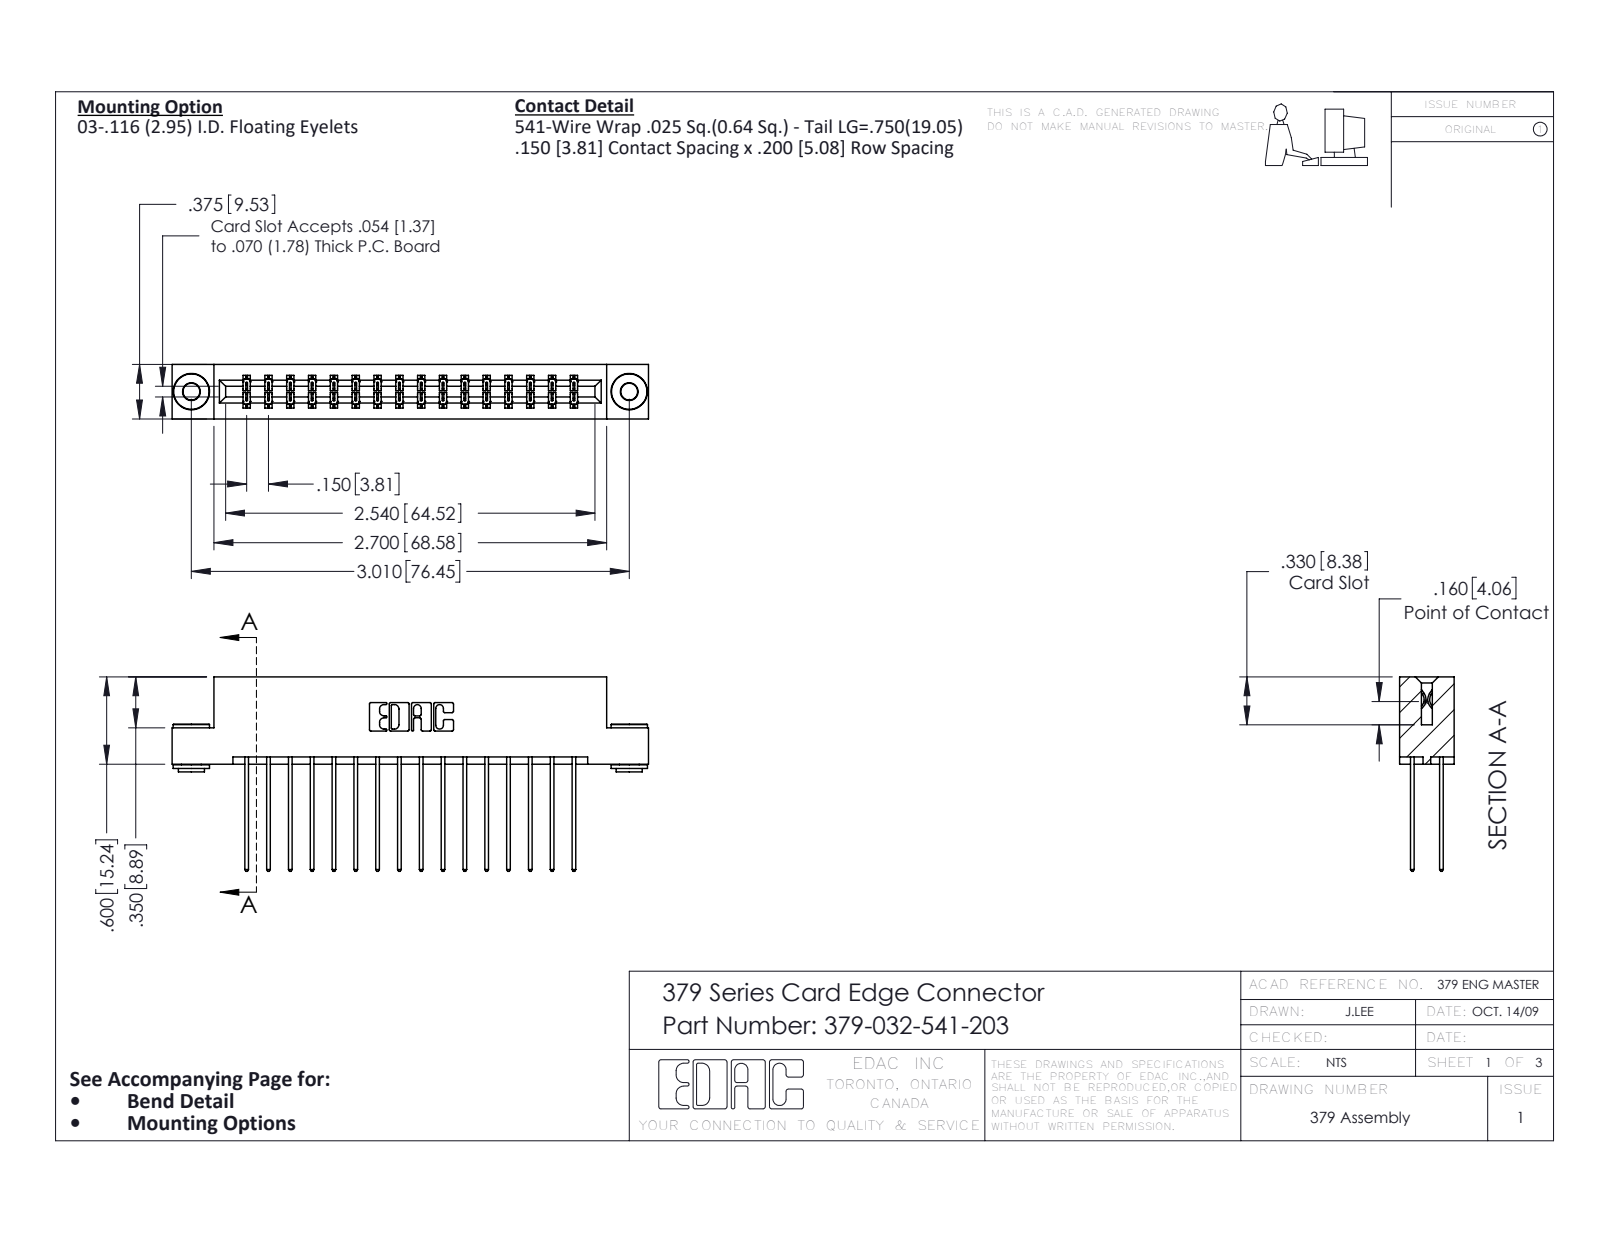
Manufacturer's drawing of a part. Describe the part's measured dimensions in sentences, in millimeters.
The part is named "345-250-002_345-250-002-102; 379-032-541-203; 345-292-001_345-293-141; 379 Part_Flush - .156 Dia - TH". Its 3-D file was written by "SolidWorks 2020 (CONFIG_CONTROL_DESIGN)". It is 35 solids with 1816 faces: 1232 planar, 576 cylindrical and 8 other. Overall it measures 83.2 by 34 by 9.5 millimeters. Its volume is 8 730 cubic millimeters and its surface area 10 720 square millimeters. Round holes: 2 of diameter 2.9, 2 of diameter 4. Round bosses or shafts: 2 of diameter 6.4, 2 of diameter 4.6, 2 of diameter 3.5. Partial cylindrical surfaces (rounded edges, fillets, slot ends): 63 of radius 0.2, 32 of radius 0.3, 22 of radius 0.3, 6 of radius 0.2, 6 of radius 0.8, 3 of radius 0.7, 2 of radius 0.4, 2 of radius 0.6. The main face-to-face distances are 7.6, 5.1, 1.9, 2.5, 9.5, 7, 0.6, 3.8, 1.3, 15.2. The hole center spacings are 76.5.
